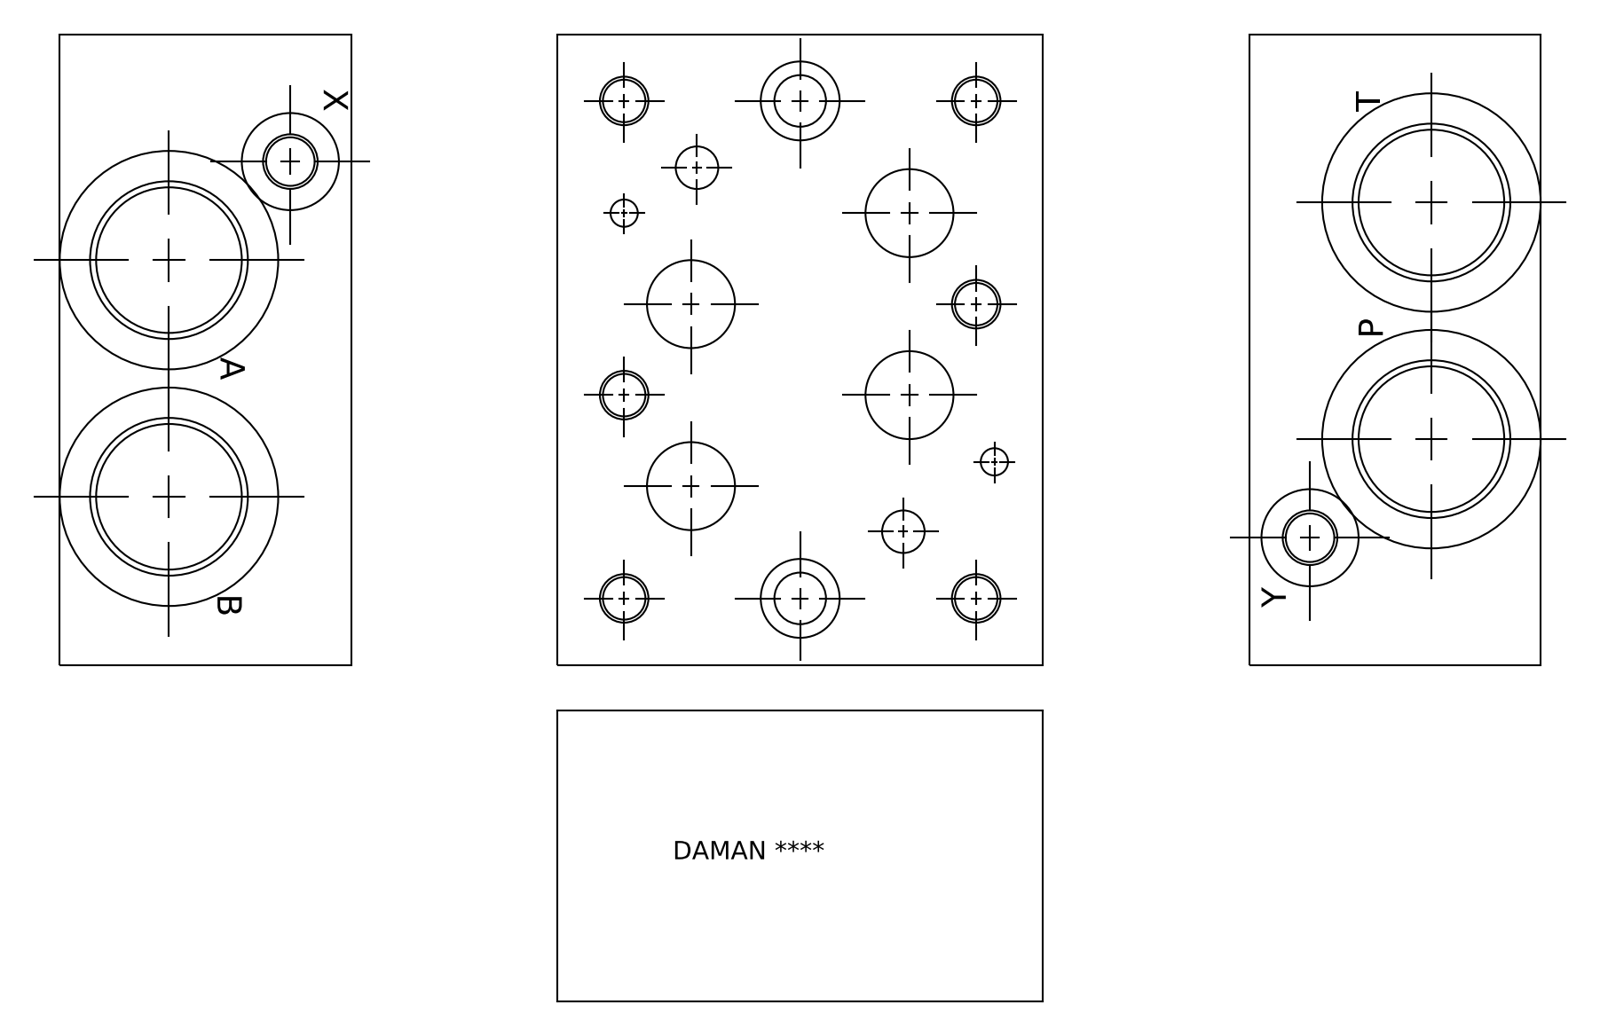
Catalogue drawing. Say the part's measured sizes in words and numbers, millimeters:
The part is named "Part_AD08SPSO20S_3D". Its 3-D file was written by "Autodesk Inventor 2020 (AUTOMOTIVE_DESIGN)". It is 1 solid with 553 faces: 297 planar, 56 cylindrical and 200 other. Overall it measures 165.1 by 127 by 76.2 millimeters. Its volume is 1 317 000 cubic millimeters and its surface area 124 374 square millimeters. Round holes: 8 of diameter 10.72, 6 of diameter 12.7, 4 of diameter 24.61, 4 of diameter 38.1, 4 of diameter 39.22, 4 of diameter 41.28, 4 of diameter 41.76, 4 of diameter 58.57, 2 of diameter 7.14, 2 of diameter 12.29, 2 of diameter 12.9, 2 of diameter 13.49. The main face-to-face distances are 76.2, 165.1, 127, 0.79, 126.21, 125.42, 19.05, 19.84, 107.16, 106.37. The hole center spacings are 29.53, 46.29, 61.93, 15.09, 25.84, 29.52, 33.52, 40.92.
